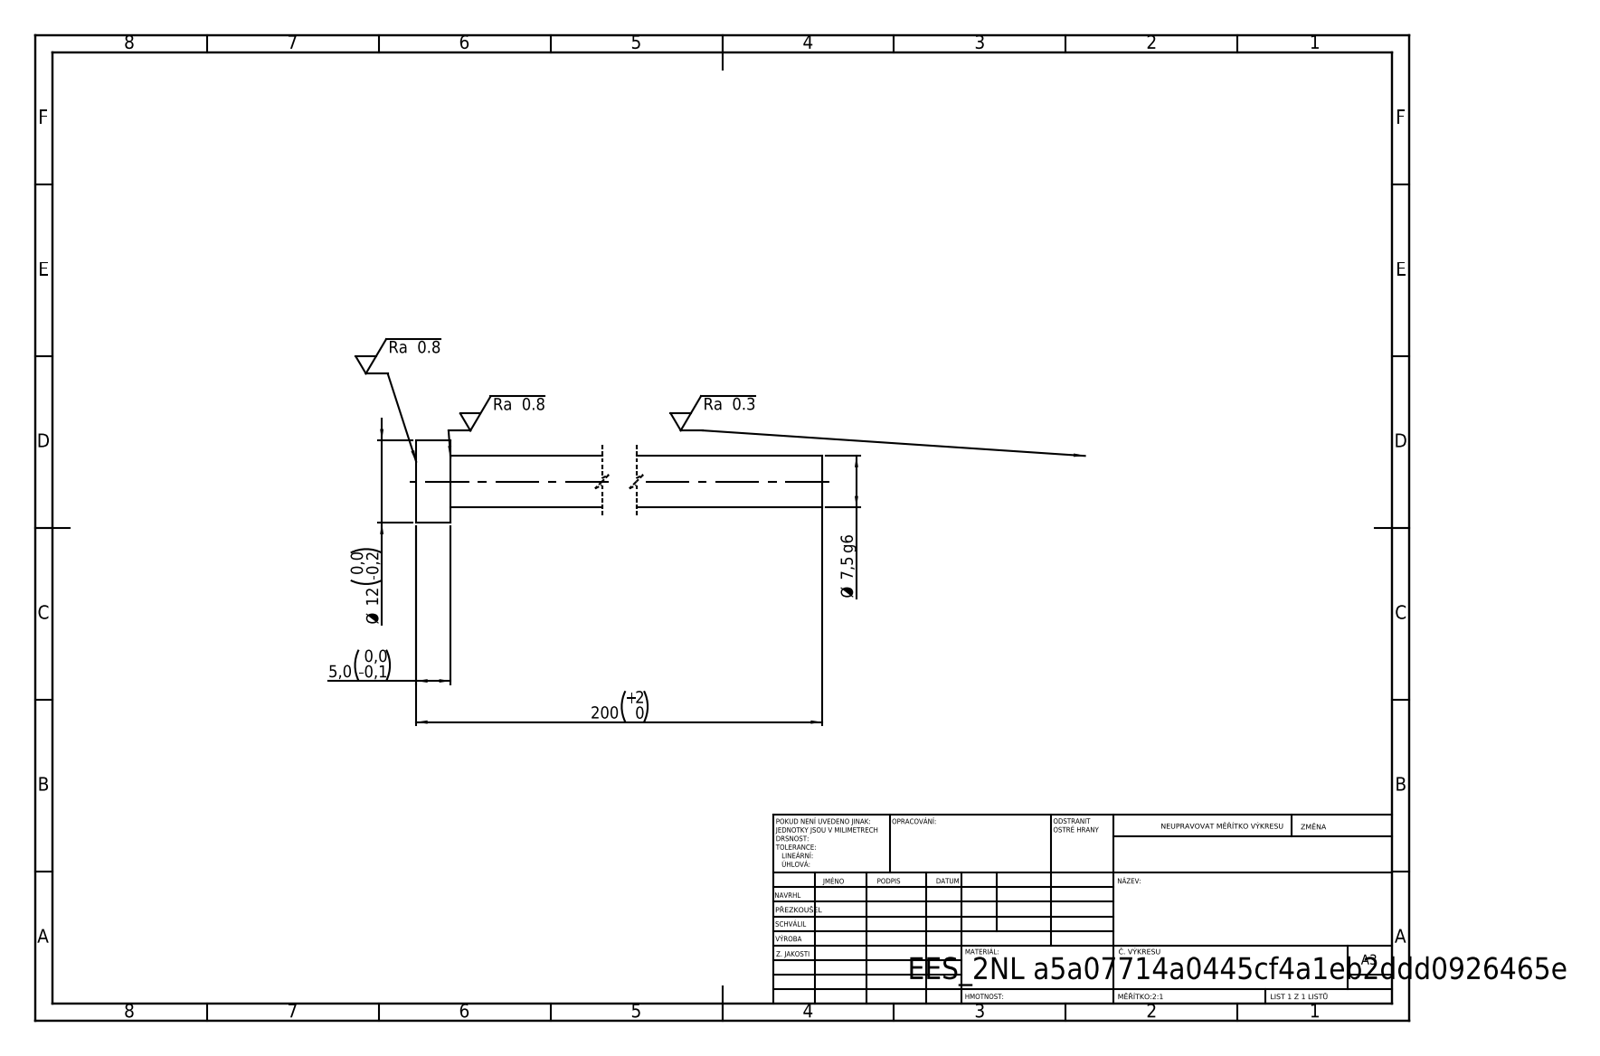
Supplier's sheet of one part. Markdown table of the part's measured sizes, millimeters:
| quantity | value |
| --- | --- |
| STEP written by | SolidWorks 2019 (CONFIG_CONTROL_DESIGN) |
| units | millimeters |
| bodies | 1 solid, 7 faces (3 planar, 4 cylindrical, 0 other) |
| overall size | 200 × 12 × 12 |
| volume | 9 180 mm³ |
| surface area | 5 009 mm² |
| round bosses / shafts (diameter × count) | 12 × 1, 7.5 × 1 |
| main face-to-face distances | 5, 200, 195 |
